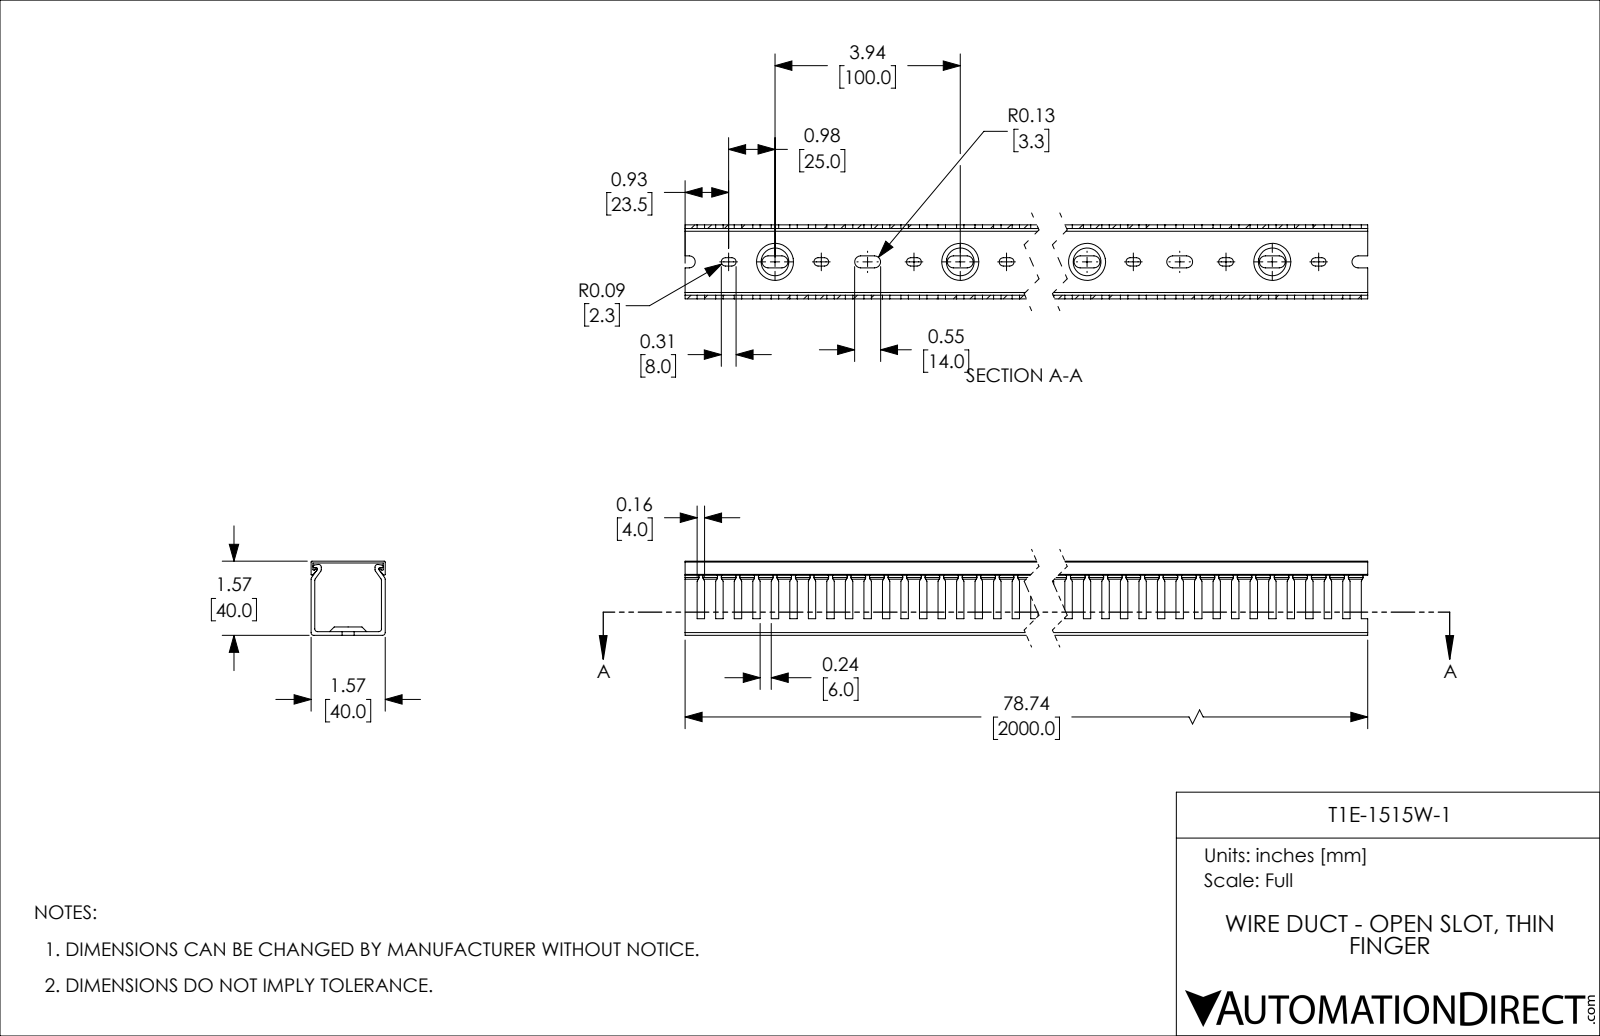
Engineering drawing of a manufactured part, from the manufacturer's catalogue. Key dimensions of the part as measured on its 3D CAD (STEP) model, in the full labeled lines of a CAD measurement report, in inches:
Part name (STEP PRODUCT): T1E-1515W-1
STEP written by: SolidWorks 2021 (CONFIG_CONTROL_DESIGN)
Units: inches
Bodies: 2 solids, 1005 faces (534 planar, 431 cylindrical, 40 other)
Overall size (bounding box): 78.74 × 1.575 × 1.575
Volume: 35.69 in³ · Surface area: 1 085 in²
Partial cylindrical surfaces — rounded edges, fillets, slot ends (radius × count): R0.089 ×80, R0.128 ×80, R0.059 ×12, R0.02 ×8, R0.03 ×6
Main face-to-face distances: 0.079, 1.496, 1.575, 0.039, 1.535, 1.457, 1.417, 0.177, 1.358, 0.217
